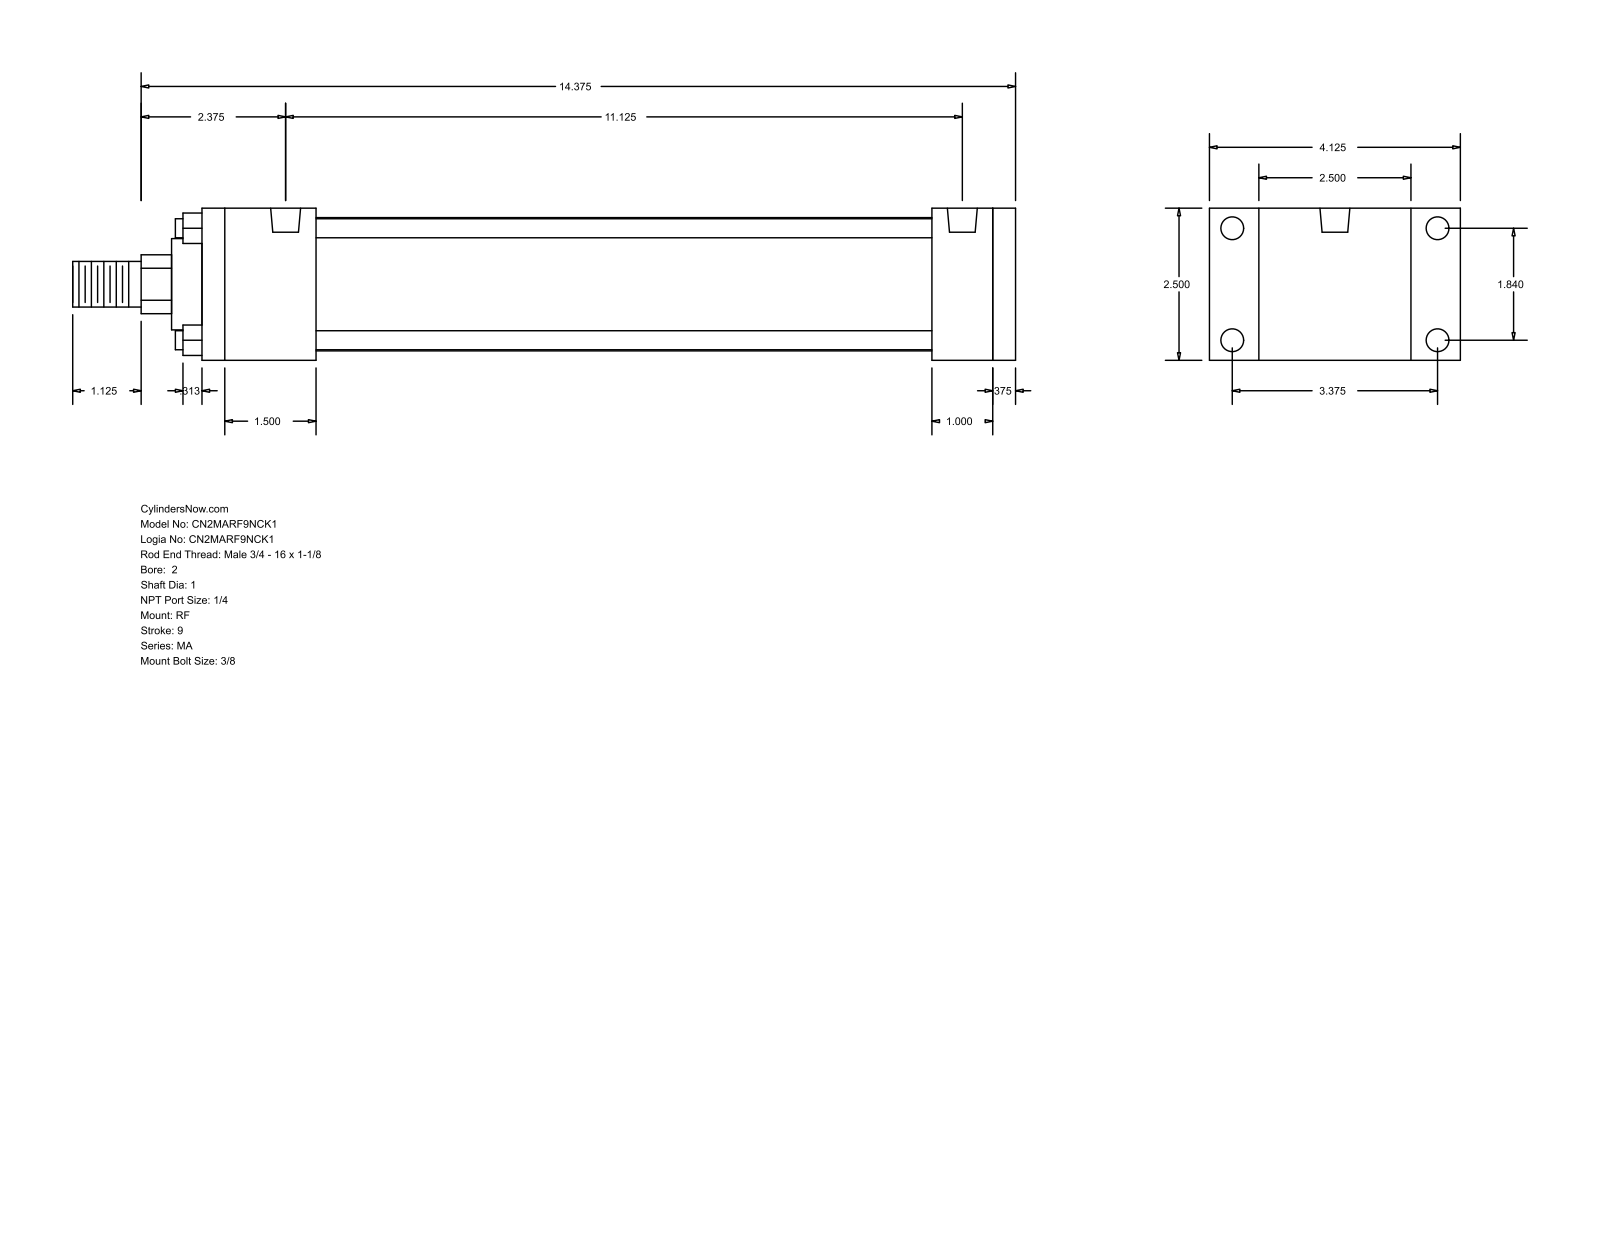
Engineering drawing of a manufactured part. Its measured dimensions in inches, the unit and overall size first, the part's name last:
Units: inches
Overall size (bounding box): 15.5 × 4.125 × 2.5
Round holes (diameter × count): ⌀0.313 ×4, ⌀0.375 ×4, ⌀0.492 ×2
Round bosses / shafts (diameter × count): ⌀0.313 ×4, ⌀2.19 ×1, ⌀1.5 ×1, ⌀1 ×1, ⌀0.75 ×1
Partial cylindrical surfaces — rounded edges, fillets, slot ends (radius × count): R0.484 ×1
Main face-to-face distances: 2.5, 13, 0.375, 13.375, 1, 0.813, 0.5, 1.875, 11.125, 11.5
Hole centre spacings: 1.84, 3.375, 3.844, 11.125
Bodies: 0 solids, 92 faces (64 planar, 28 cylindrical, 0 other)
Part name (STEP PRODUCT): MA_RF__0200_1
STEP written by: GSSL Pune (CONFIG_CONTROL_DESIGN)
